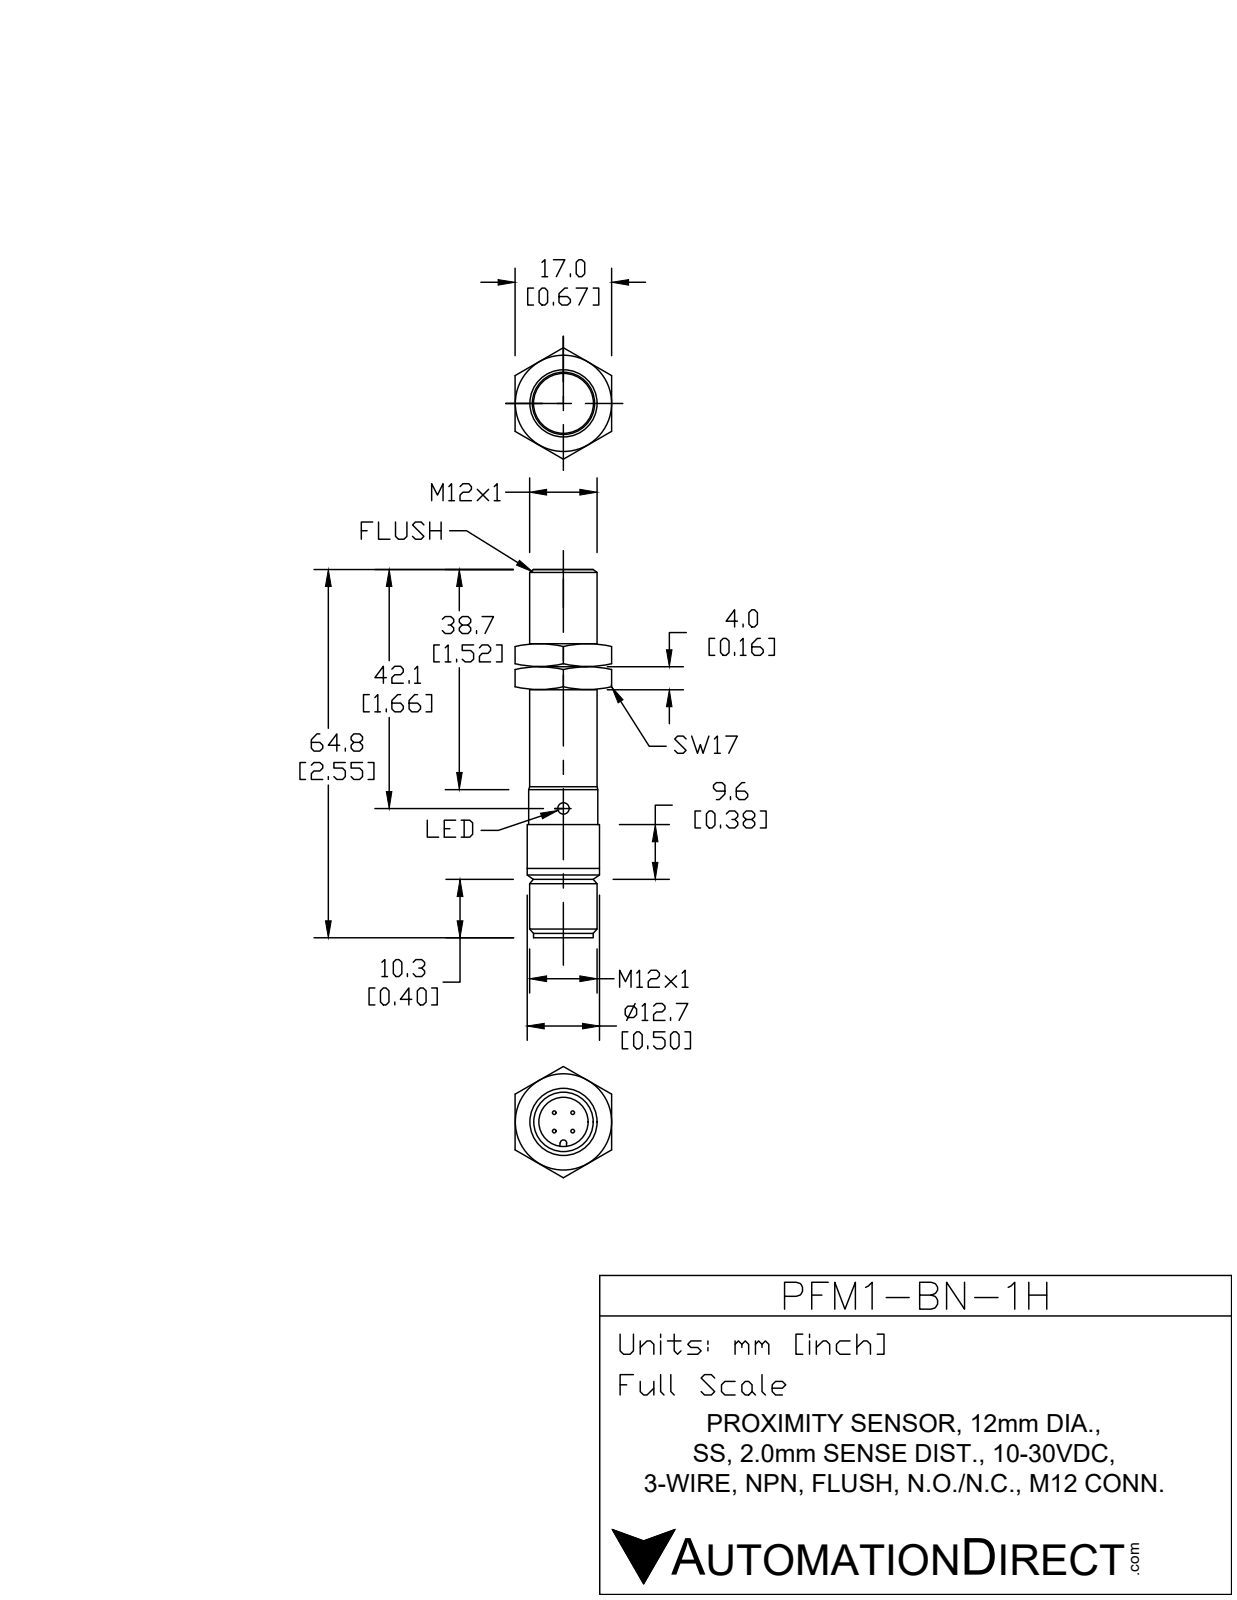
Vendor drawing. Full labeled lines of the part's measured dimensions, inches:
Part name (STEP PRODUCT): PFM1-BN-1H
STEP written by: SolidWorks 2017 (AUTOMOTIVE_DESIGN)
Units: inches
Bodies: 3 solids, 70 faces (10 planar, 36 cylindrical, 24 other)
Overall size (bounding box): 2.543 × 0.5 × 0.5
Volume: 0.422 in³ · Surface area: 6.12 in²
Round holes (diameter × count): ⌀0.118 ×1, ⌀0.331 ×1, ⌀0.335 ×1, ⌀0.374 ×1
Round bosses / shafts (diameter × count): ⌀0.039 ×4, ⌀0.5 ×1, ⌀0.472 ×1, ⌀0.413 ×1, ⌀0.396 ×1, ⌀0.37 ×1
Partial cylindrical surfaces — rounded edges, fillets, slot ends (radius × count): R0.024 ×1, R0.219 ×1
Main face-to-face distances: 0.071, 2.075, 2.146, 2.193, 0.118, 0.047, 2.504, 0.429, 0.358, 0.311
